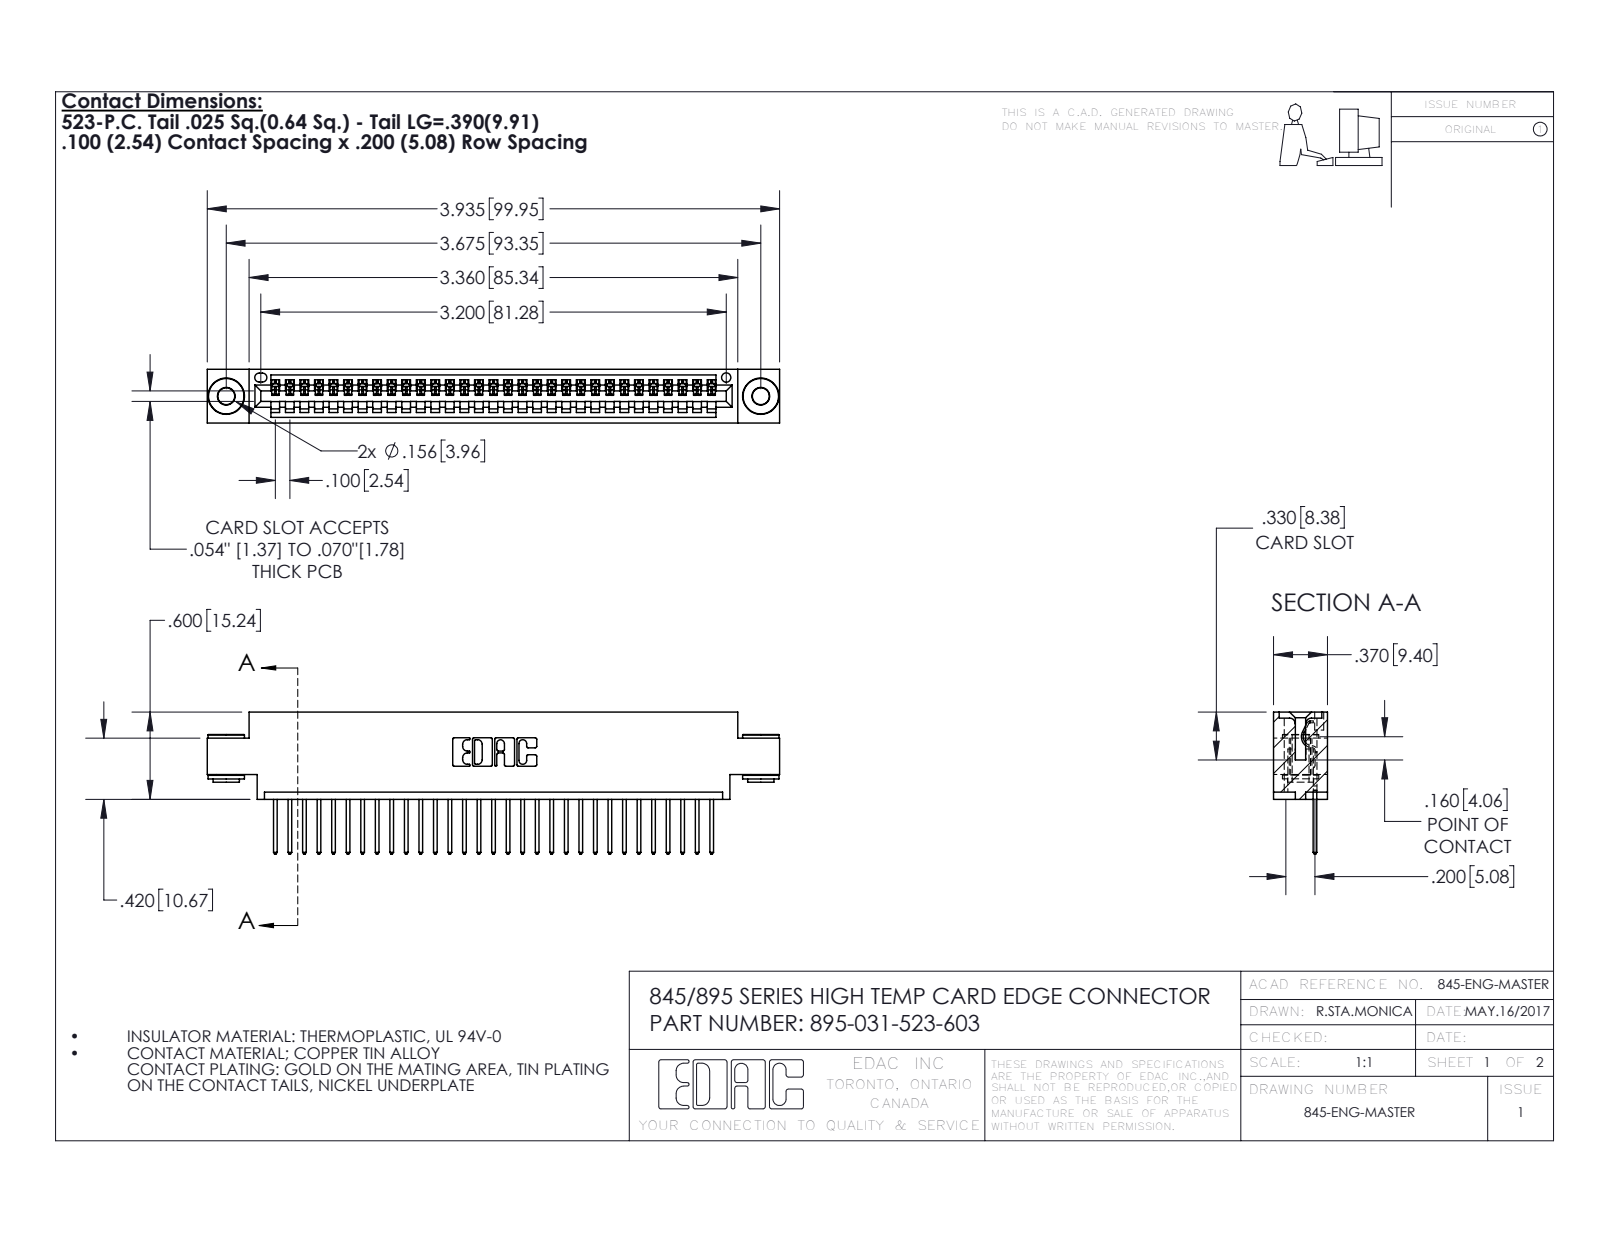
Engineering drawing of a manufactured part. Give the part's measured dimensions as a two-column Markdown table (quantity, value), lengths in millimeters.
| quantity | value |
| --- | --- |
| part name | 345-292-001_345-293-123; 345 Part_0.170 Offset - 0.156 Dia-TH; 345-250-002_345-250-002-102; 395-031-523-603 |
| STEP written by | SolidWorks 2016 (CONFIG_CONTROL_DESIGN) |
| units | millimeters |
| bodies | 34 solids, 1966 faces (1334 planar, 624 cylindrical, 8 other) |
| overall size | 99.9 × 24.8 × 9.4 |
| volume | 9 290 mm³ |
| surface area | 12 580 mm² |
| round holes (diameter × count) | 2.9 × 2, 4 × 2, 1.6 × 1 |
| round bosses / shafts (diameter × count) | 6.4 × 2, 4.6 × 2, 3.5 × 2 |
| partial cylindrical surfaces (radius × count) | 0.2 × 62, 0.3 × 62, 0.3 × 22, 0.2 × 6, 0.8 × 6, 0.7 × 3, 0.8 × 2, 1 × 2 |
| main face-to-face distances | 1.8, 7.6, 9.4, 5.1, 2.5, 6.9, 0.6, 5.7, 4.4, 3.8 |
| hole center spacings | 6.9, 87.4, 93.3 |
